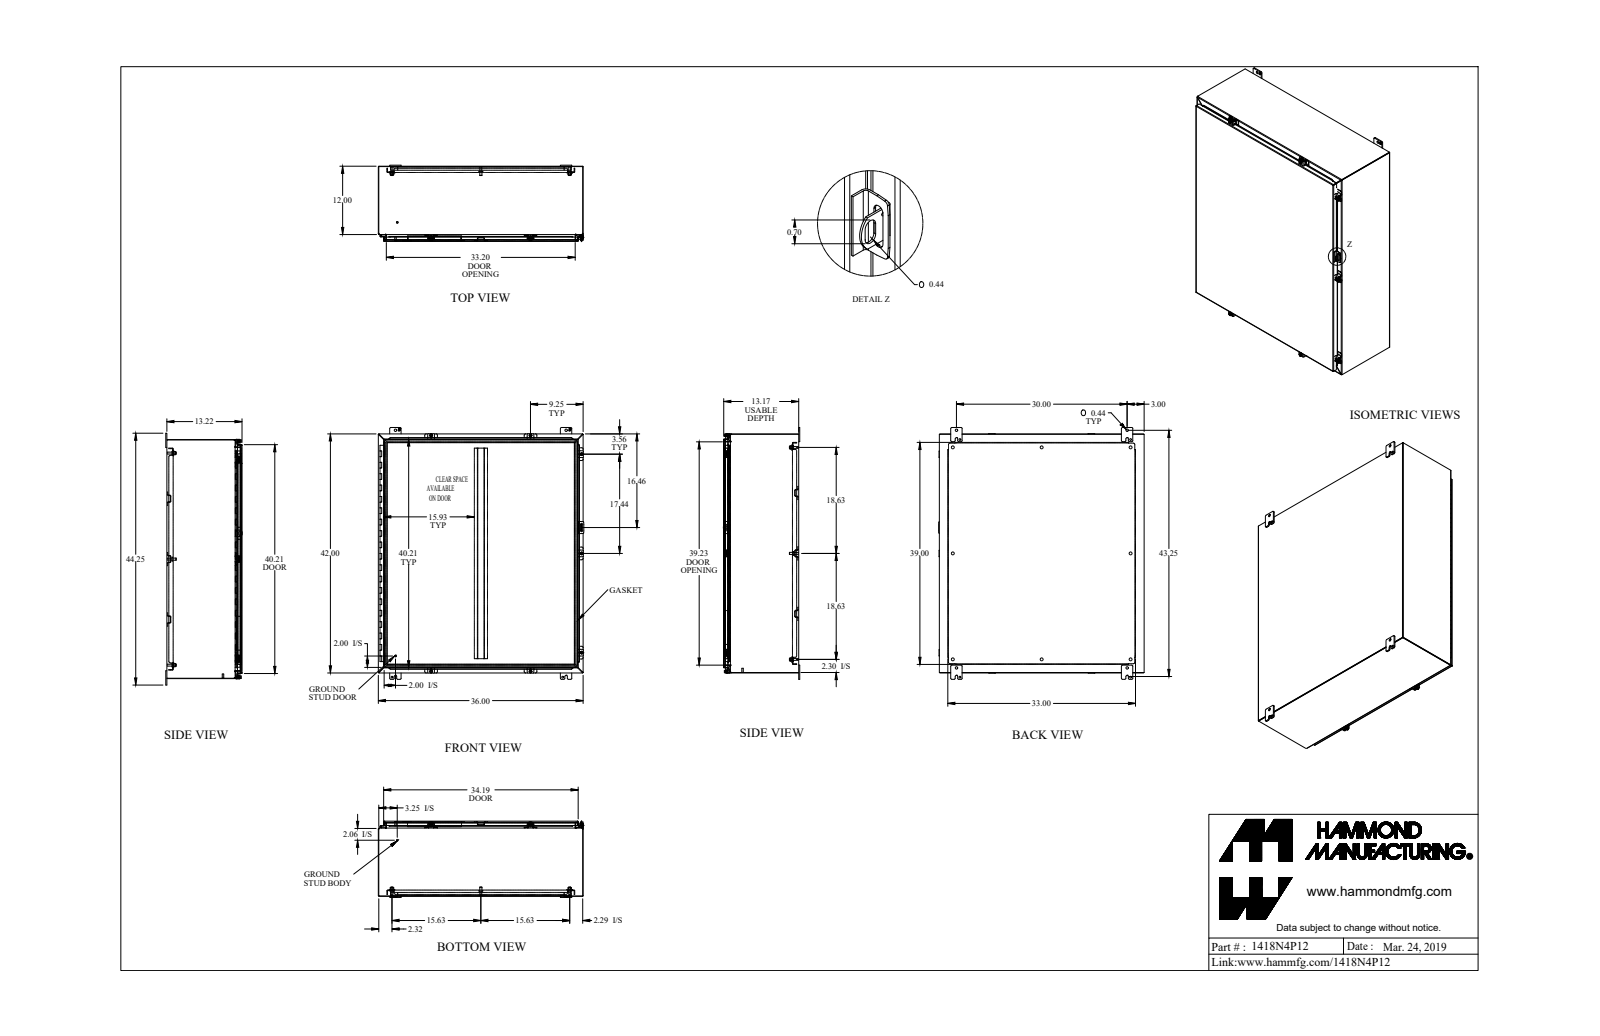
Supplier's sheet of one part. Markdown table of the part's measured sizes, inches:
| quantity | value |
| --- | --- |
| part name | 1418N4P12_Default |
| STEP written by | SolidWorks 2019 (CONFIG_CONTROL_DESIGN) |
| units | inches |
| bodies | 71 solids, 2166 faces (1309 planar, 749 cylindrical, 108 other) |
| overall size | 44.25 × 36.144 × 13.437 |
| volume | 549.4 in³ |
| surface area | 14 426 in² |
| round holes (diameter × count) | 0.307 × 8, 0.445 × 8, 0.5 × 8, 0.213 × 7, 0.285 × 7, 0.375 × 7, 0.313 × 4, 0.437 × 4, 0.125 × 1, 0.187 × 1, 0.2 × 1 |
| round bosses / shafts (diameter × count) | 1 × 8, 0.65 × 8, 0.375 × 8, 0.33 × 8, 0.39 × 7, 0.244 × 7, 0.625 × 4, 0.625 × 3 |
| partial cylindrical surfaces (radius × count) | 0.25 × 48, 0.048 × 45, 0.188 × 40, 0.143 × 33, 0.116 × 16, 0.141 × 14, 0.12 × 12, 0.125 × 12 |
| main face-to-face distances | 0.072, 13.113, 0.072, 13.041, 13.185, 0.095, 12.081, 12.009, 1.032, 1.104 |
| hole center spacings | 15.625, 40.394, 31.25, 15.625, 24.311, 37.25, 40.394, 7.196 |
